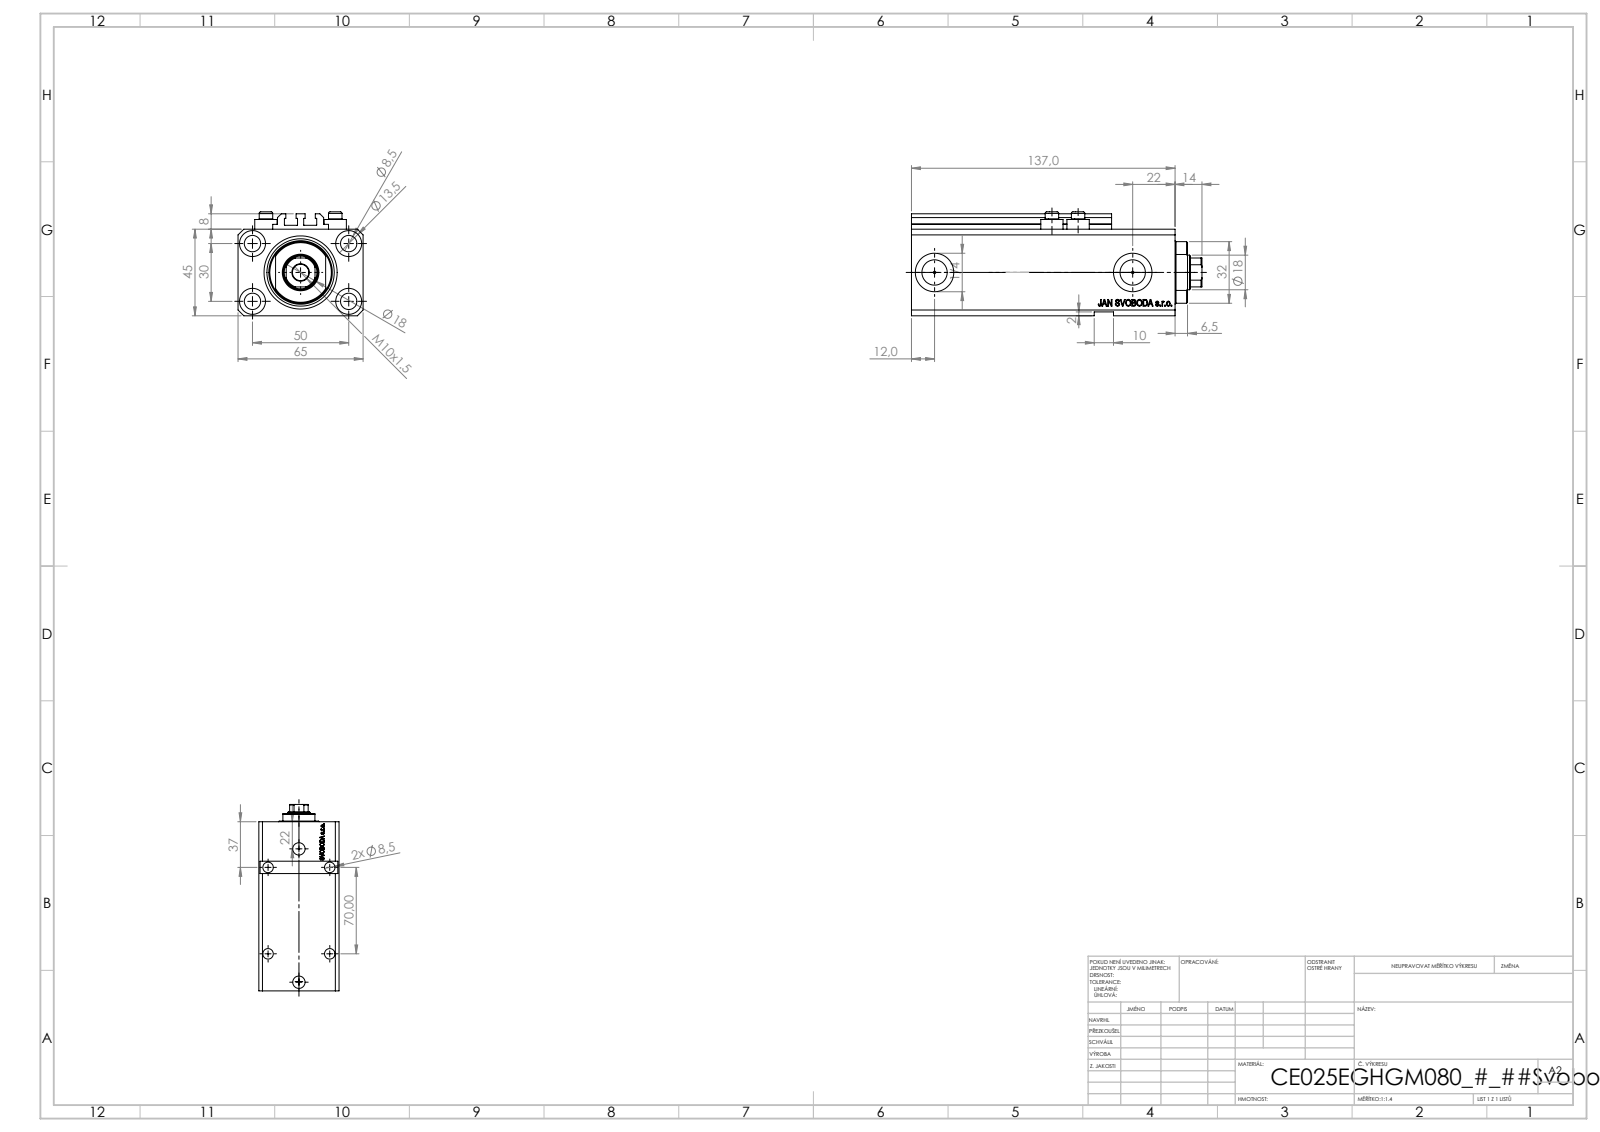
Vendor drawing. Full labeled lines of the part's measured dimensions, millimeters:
Part name (STEP PRODUCT): V250CE_E_Body; V250CE_C_VCP; V250CE_VC_E; ALLEN BOLT V250CE
STEP written by: SolidWorks 2019 (CONFIG_CONTROL_DESIGN)
Units: millimetres
Bodies: 8 solids, 1087 faces (511 planar, 146 cylindrical, 430 other)
Overall size (bounding box): 151 × 65 × 54
Volume: 350 493 mm³ · Surface area: 93 546 mm²
Round holes (diameter × count): ⌀8.5 ×9, ⌀1.25 ×4, ⌀4 ×4, ⌀13.5 ×4, ⌀10 ×2, ⌀13.16 ×2, ⌀20 ×2, ⌀18 ×1, ⌀25 ×1, ⌀38 ×1
Round bosses / shafts (diameter × count): ⌀11.6 ×4, ⌀7 ×4
Partial cylindrical surfaces — rounded edges, fillets, slot ends (radius × count): R0.2 ×10, R8.5 ×1, R16 ×1
Main face-to-face distances: 45, 65, 47, 2, 123, 2.5, 14, 10, 137, 20.5
Hole centre spacings: 29.15, 50, 13.6, 15.12, 27.89, 30, 33.61, 33.62
